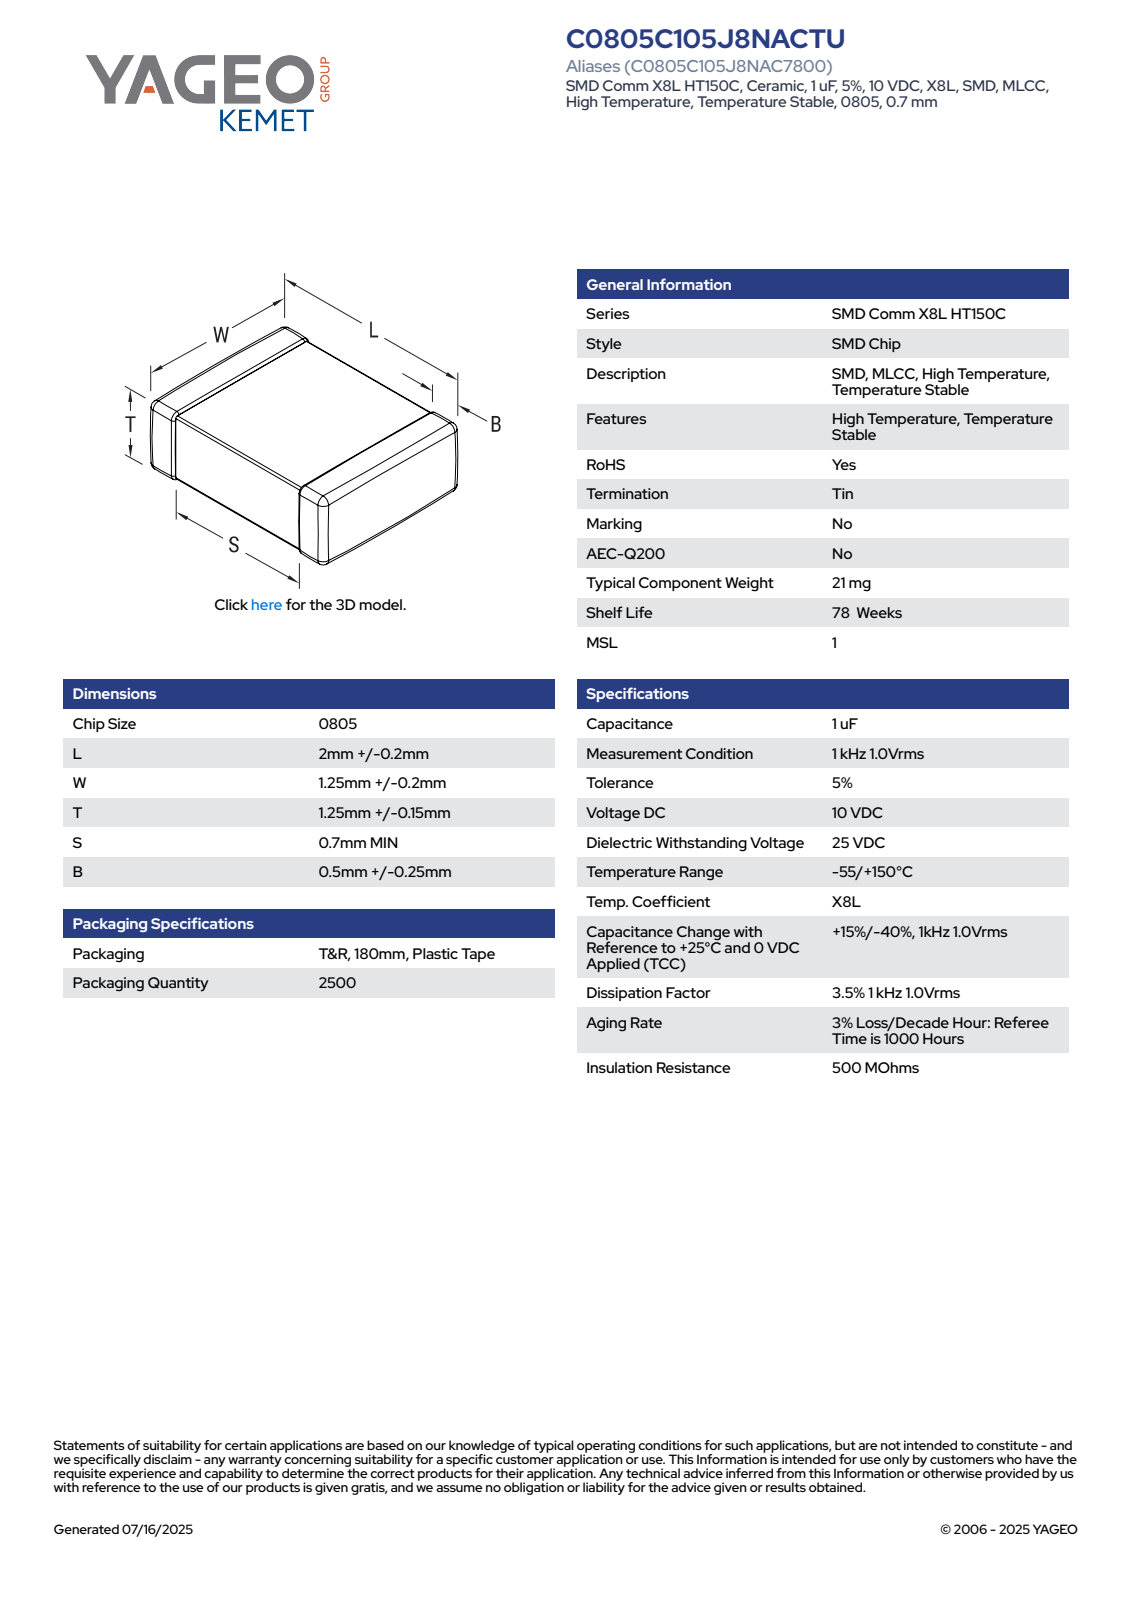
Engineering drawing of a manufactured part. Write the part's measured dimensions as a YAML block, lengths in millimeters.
part_name: "CCS_CCSTD_0805_L2.2W1.45S1.25T1.4B0.5"
step_written_by: "SolidWorks 2021 (AUTOMOTIVE_DESIGN)"
units: millimeters
bodies: {solids: 4, faces: 121, planar: 71, cylindrical: 34, other: 16}
overall_size: [2.2, 1.45, 1.4]
volume: 4
surface_area: 17
face_to_face_distances: [1.37, 1.4, 2.2, 1.45, 1.42, 1.34, 1.39, 0.97, 1.23, 1.19]
